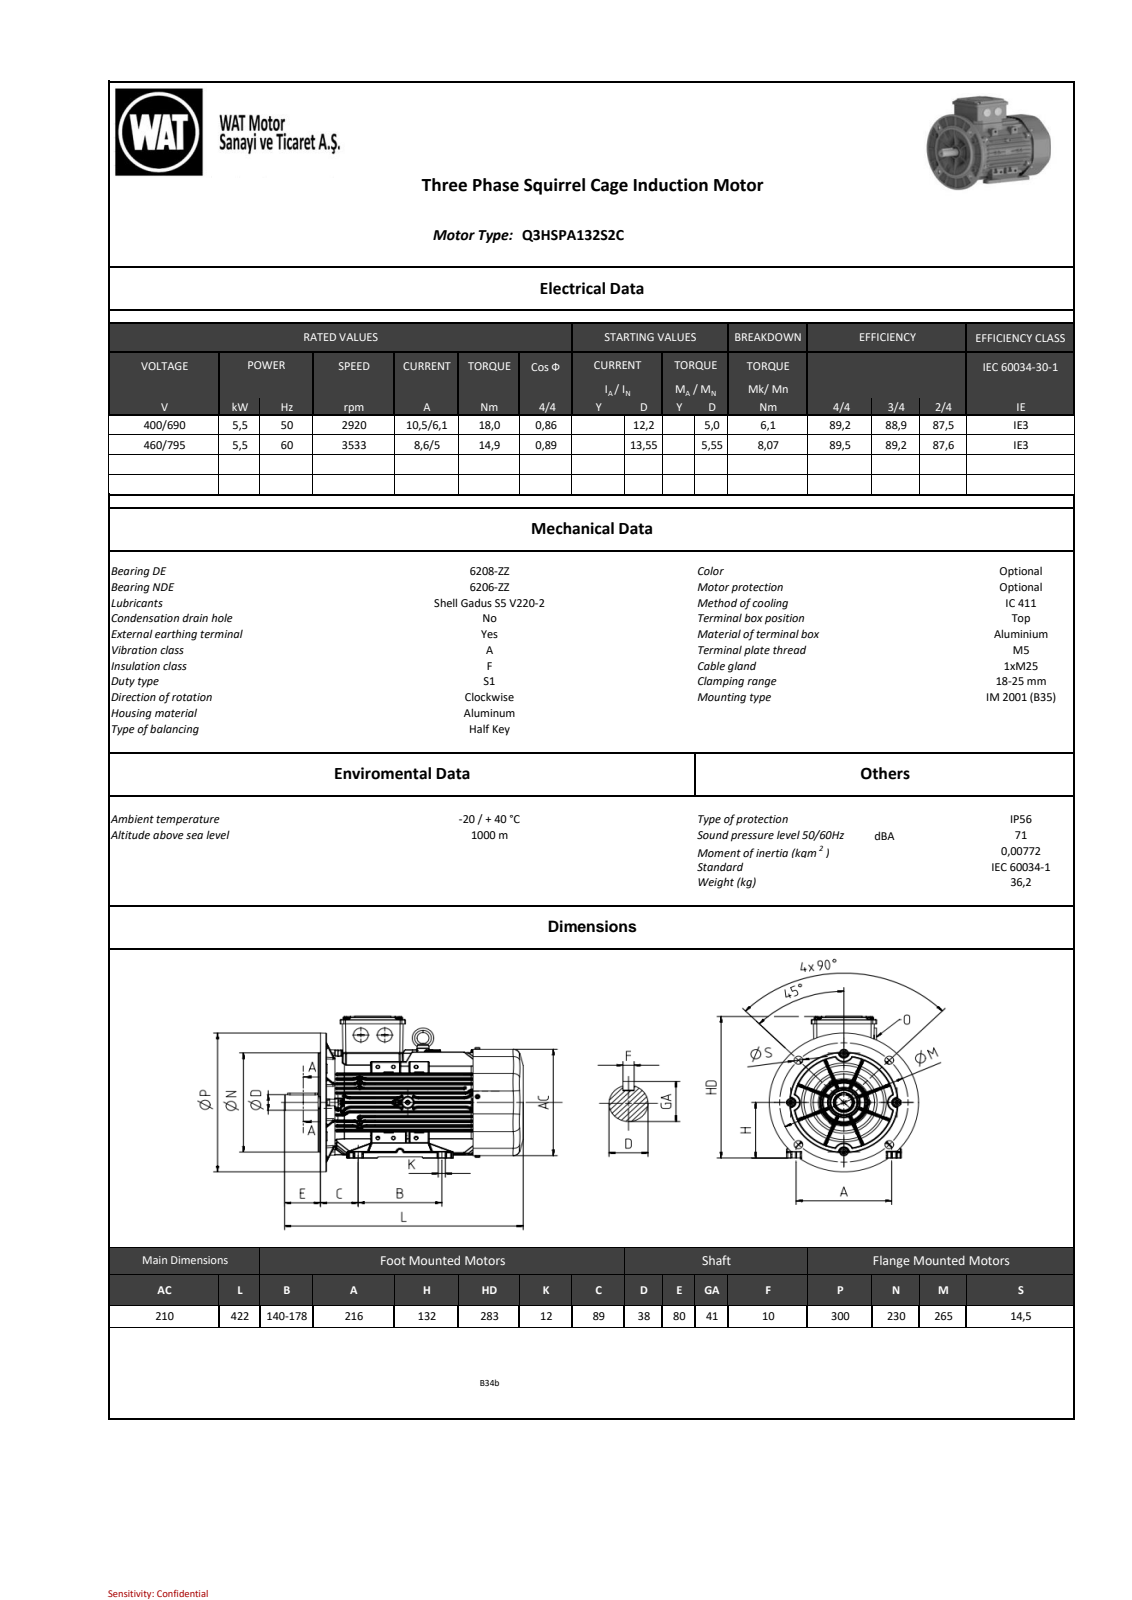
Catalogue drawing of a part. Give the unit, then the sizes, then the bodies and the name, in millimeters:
Units: millimetres
Overall size (bounding box): 422 × 301.09 × 300.25
Round holes (diameter × count): ⌀6.65 ×4, ⌀8.3 ×4, ⌀12 ×2, ⌀27.8 ×2, ⌀4 ×1, ⌀4.72 ×1, ⌀5 ×1, ⌀8 ×1, ⌀10.3 ×1, ⌀13 ×1, ⌀23.38 ×1, ⌀57.4 ×1
Round bosses / shafts (diameter × count): ⌀8 ×12, ⌀14.8 ×4, ⌀13 ×4, ⌀11.8 ×4, ⌀10 ×4, ⌀6 ×4, ⌀230 ×1, ⌀188 ×1
Partial cylindrical surfaces — rounded edges, fillets, slot ends (radius × count): R0.5 ×716, R1 ×573, R0.8 ×468, R2 ×218, R3 ×50, R0.3 ×14, R0.38 ×13, R5 ×13
Main face-to-face distances: 21.2, 1, 5, 21.5, 35.96, 10.99, 99.54, 24.97, 112.88, 8.16
Hole centre spacings: 40, 110, 72.62, 123.63, 144, 181.21, 49.5, 57.87
Bodies: 0 solids, 10352 faces (2052 planar, 3112 cylindrical, 5188 other)
Part name (STEP PRODUCT): Ar311510F80552yr
STEP written by: SIEMENS PLM Software NX 9.0 (AUTOMOTIVE_DESIGN)
